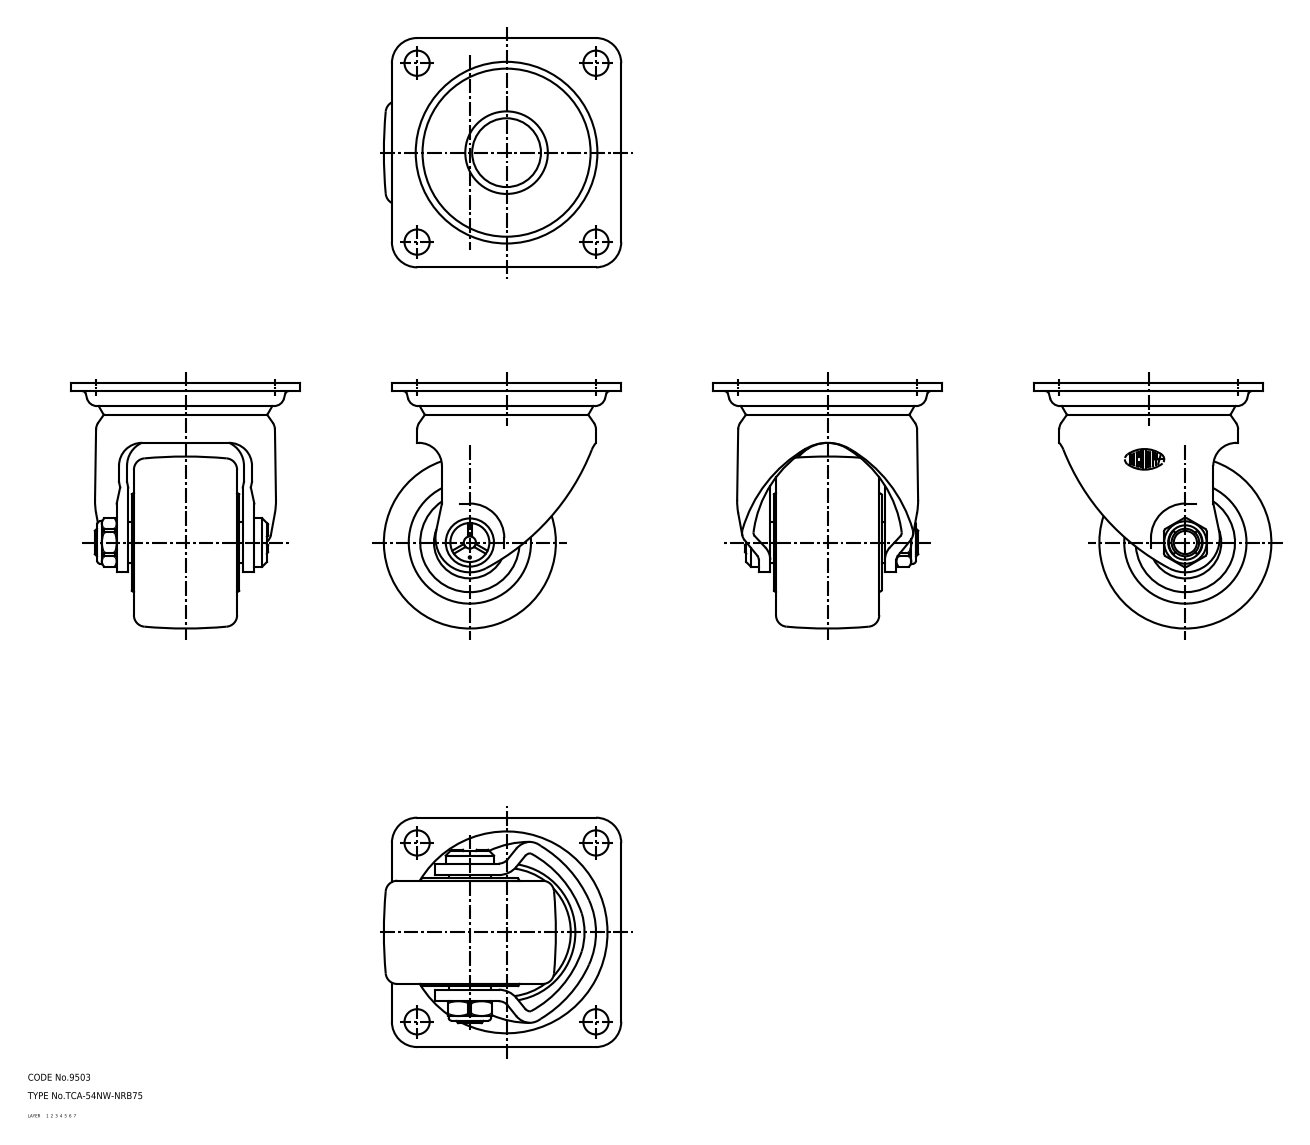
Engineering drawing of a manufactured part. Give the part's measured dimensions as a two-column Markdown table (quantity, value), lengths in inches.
| quantity | value |
| --- | --- |
| part name | wheel; seal; nut; mounting plate (+3 more) |
| STEP written by | CADfix (AUTOMOTIVE_DESIGN) |
| units | inches |
| bodies | 7 solids, 283 faces (0 planar, 0 cylindrical, 283 other) |
| overall size | 4.213 × 4.075 × 3.937 |
| volume | 20.85 in³ |
| surface area | 136.7 in² |
